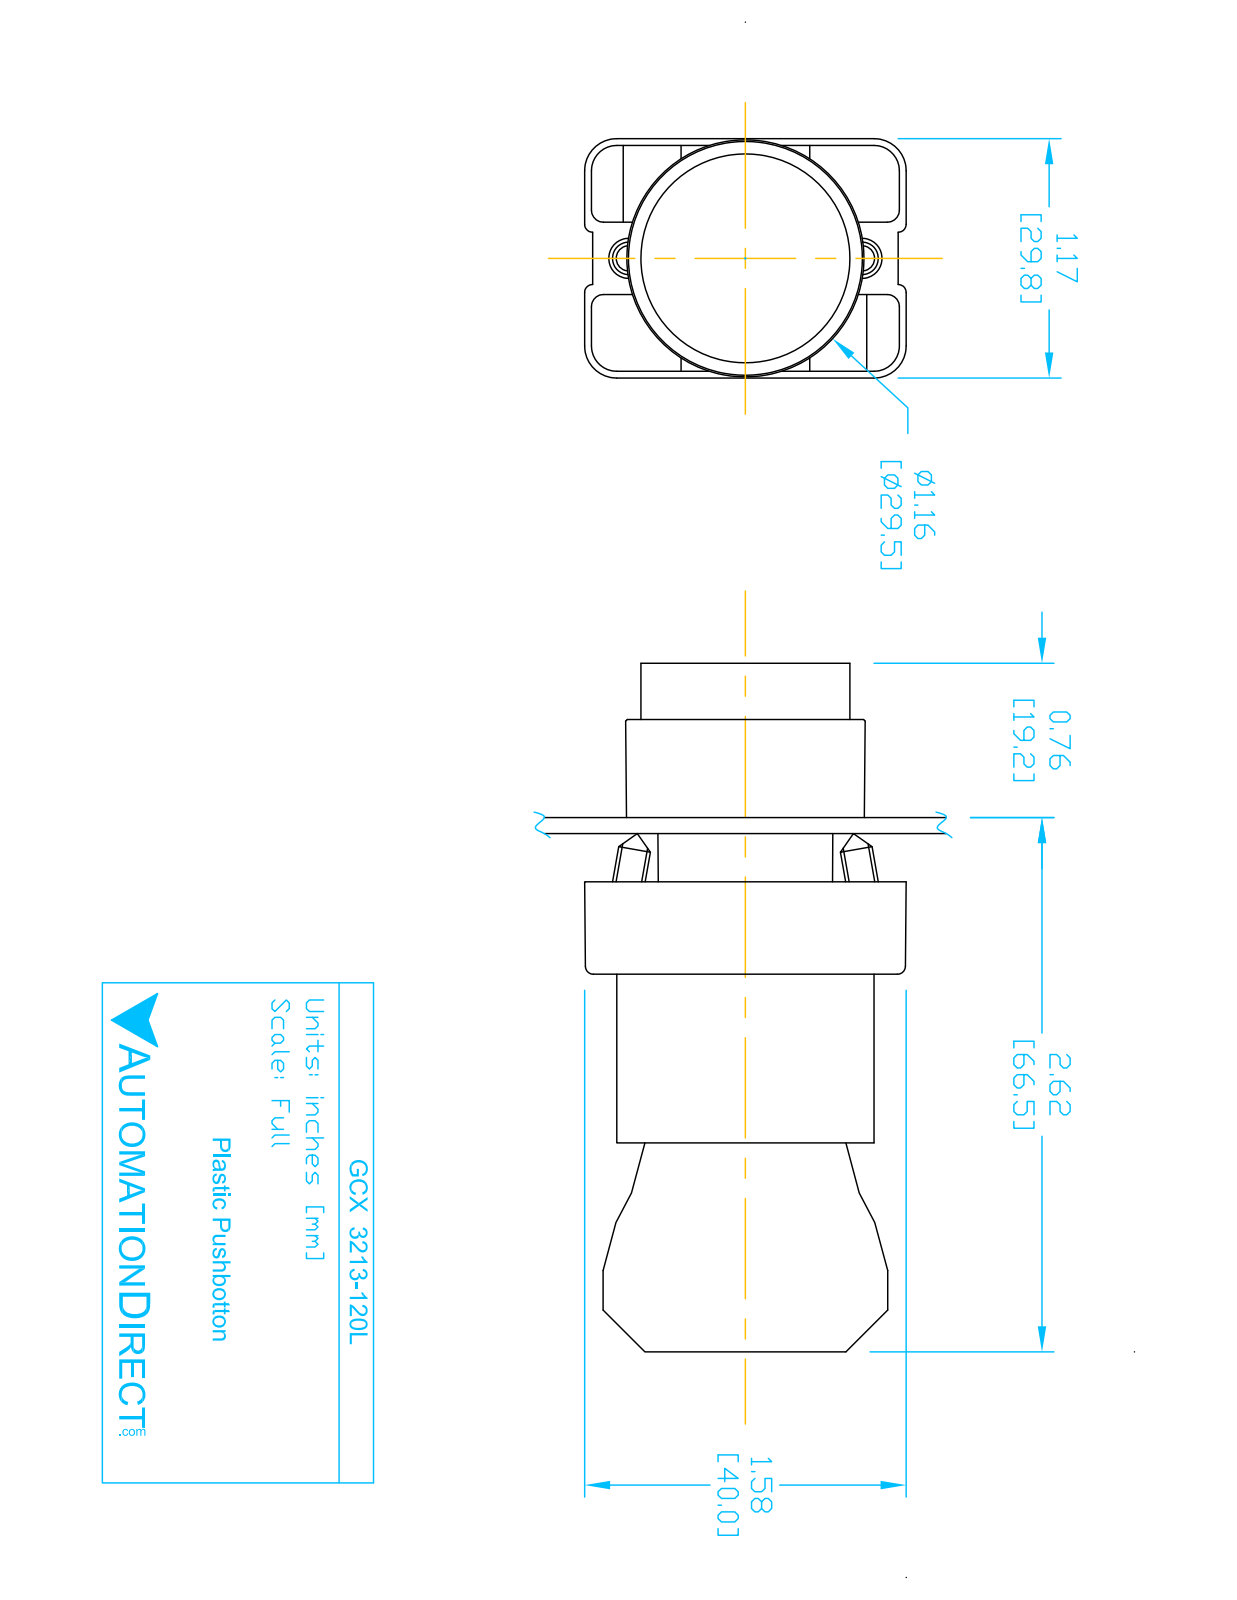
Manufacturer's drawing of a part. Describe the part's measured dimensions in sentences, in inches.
The part is named "ECX3029-2; ecx1040; ECX1050; GCX3213L OPERATOR (+1 more)". Its 3-D file was written by "SolidWorks 2016 (AUTOMOTIVE_DESIGN)". It is 7 solids with 425 faces: 250 planar, 144 cylindrical and 31 other. Overall it measures 3.319 by 1.581 by 1.177 inches. Its volume is 2.721 cubic inches and its surface area 36.32 square inches. Round holes: 2 of diameter 0.079, 2 of diameter 0.124, 2 of diameter 0.13, 1 of diameter 0.087, 1 of diameter 0.197, 1 of diameter 0.469, 1 of diameter 0.878, 1 of diameter 0.888, 1 of diameter 1.024. Round bosses or shafts: 4 of diameter 0.157, 1 of diameter 1.175, 1 of diameter 1.004, 1 of diameter 0.945, 1 of diameter 0.856, 1 of diameter 0.78, 1 of diameter 0.504. Partial cylindrical surfaces (rounded edges, fillets, slot ends): 24 of radius 0.059, 12 of radius 0.041, 12 of radius 0.124, 12 of radius 0.157, 8 of radius 0.039, 2 of radius 0.128, 1 of radius 0.02, 1 of radius 0.063. The main face-to-face distances are 0.827, 0.579, 1.171, 2.02, 1.193, 0.031, 0.033, 0.573, 1.165, 0.593. The hole center spacings are 0.236, 0.544, 0.472, 0.49.
